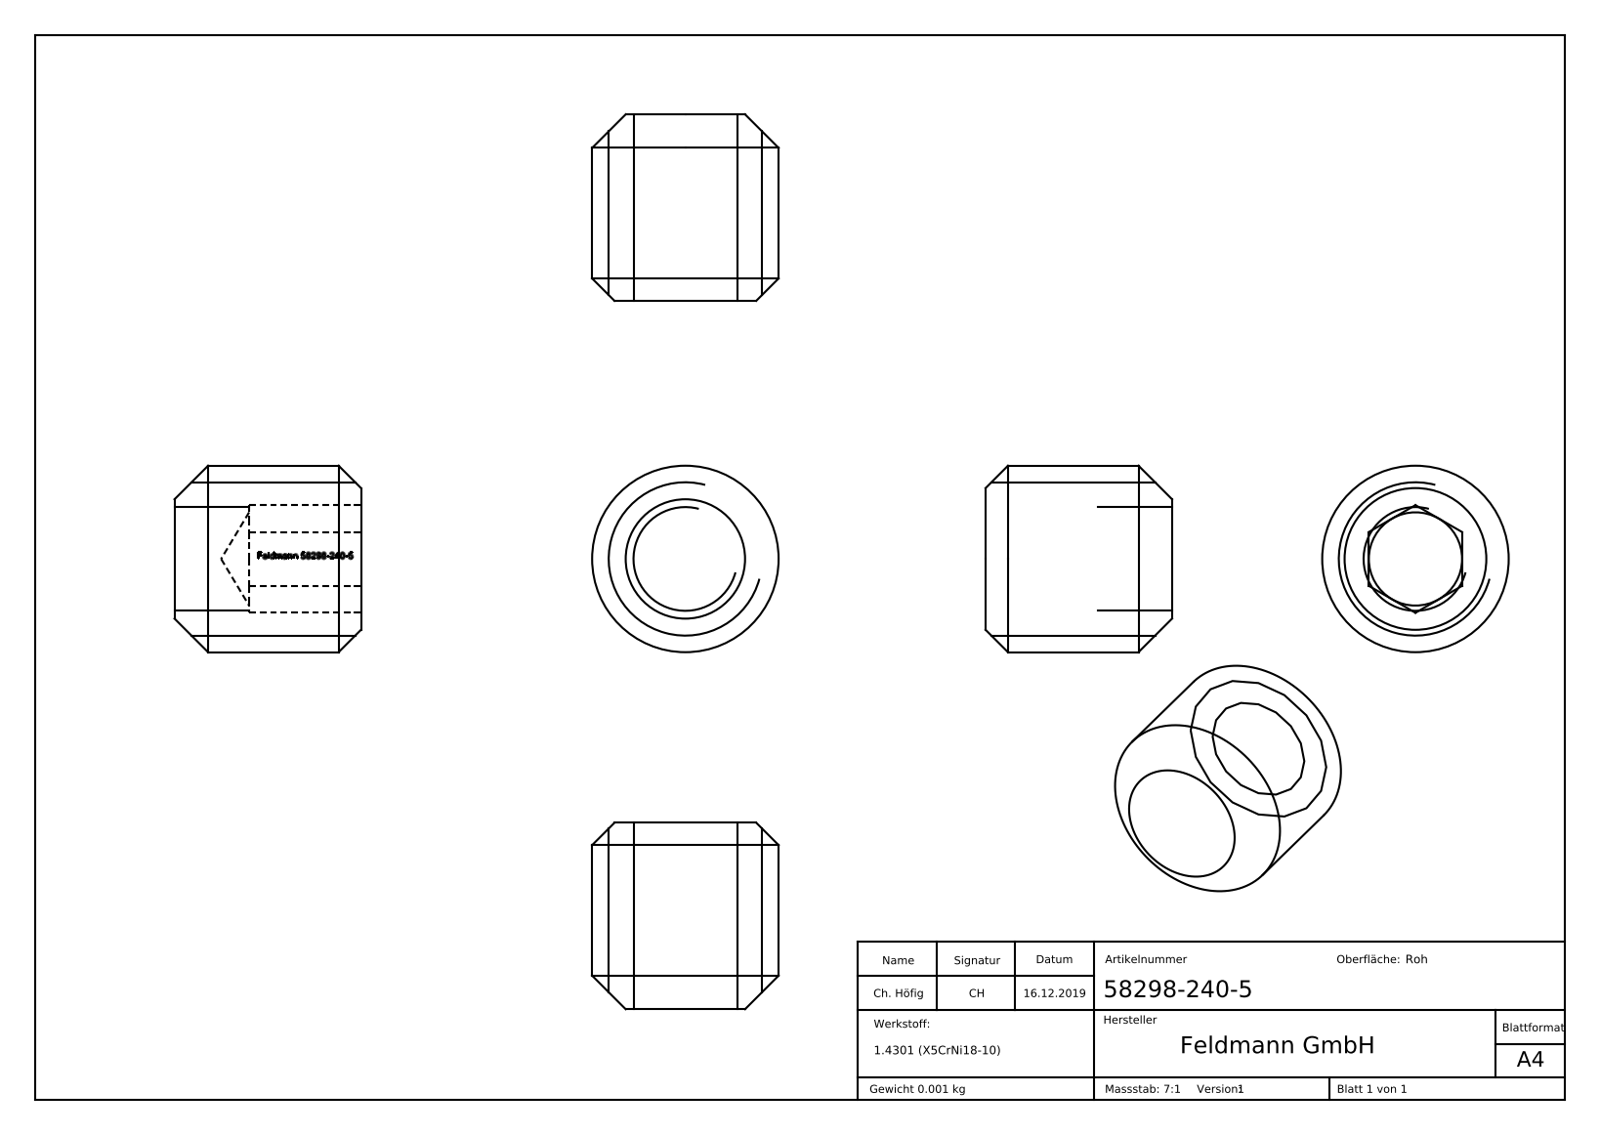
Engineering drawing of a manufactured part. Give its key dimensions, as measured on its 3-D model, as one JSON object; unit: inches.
{"part_name": "58298-240-5", "step_written_by": "SolidWorks 2015 (CONFIG_CONTROL_DESIGN)", "units": "inches", "bodies": {"solids": 1, "faces": 291, "planar": 141, "cylindrical": 1, "other": 149}, "overall_size": [2.756, 0.197, 0.197], "volume_in3": 0.004, "surface_area_in2": 0.203, "round_bosses_or_shafts": [[0.197, 1]], "face_to_face_distances": [0.098, 0.197, 0.079, 0.118, 0.102, 0.021, 0.019, 0.047, 0.02, 0.026]}
